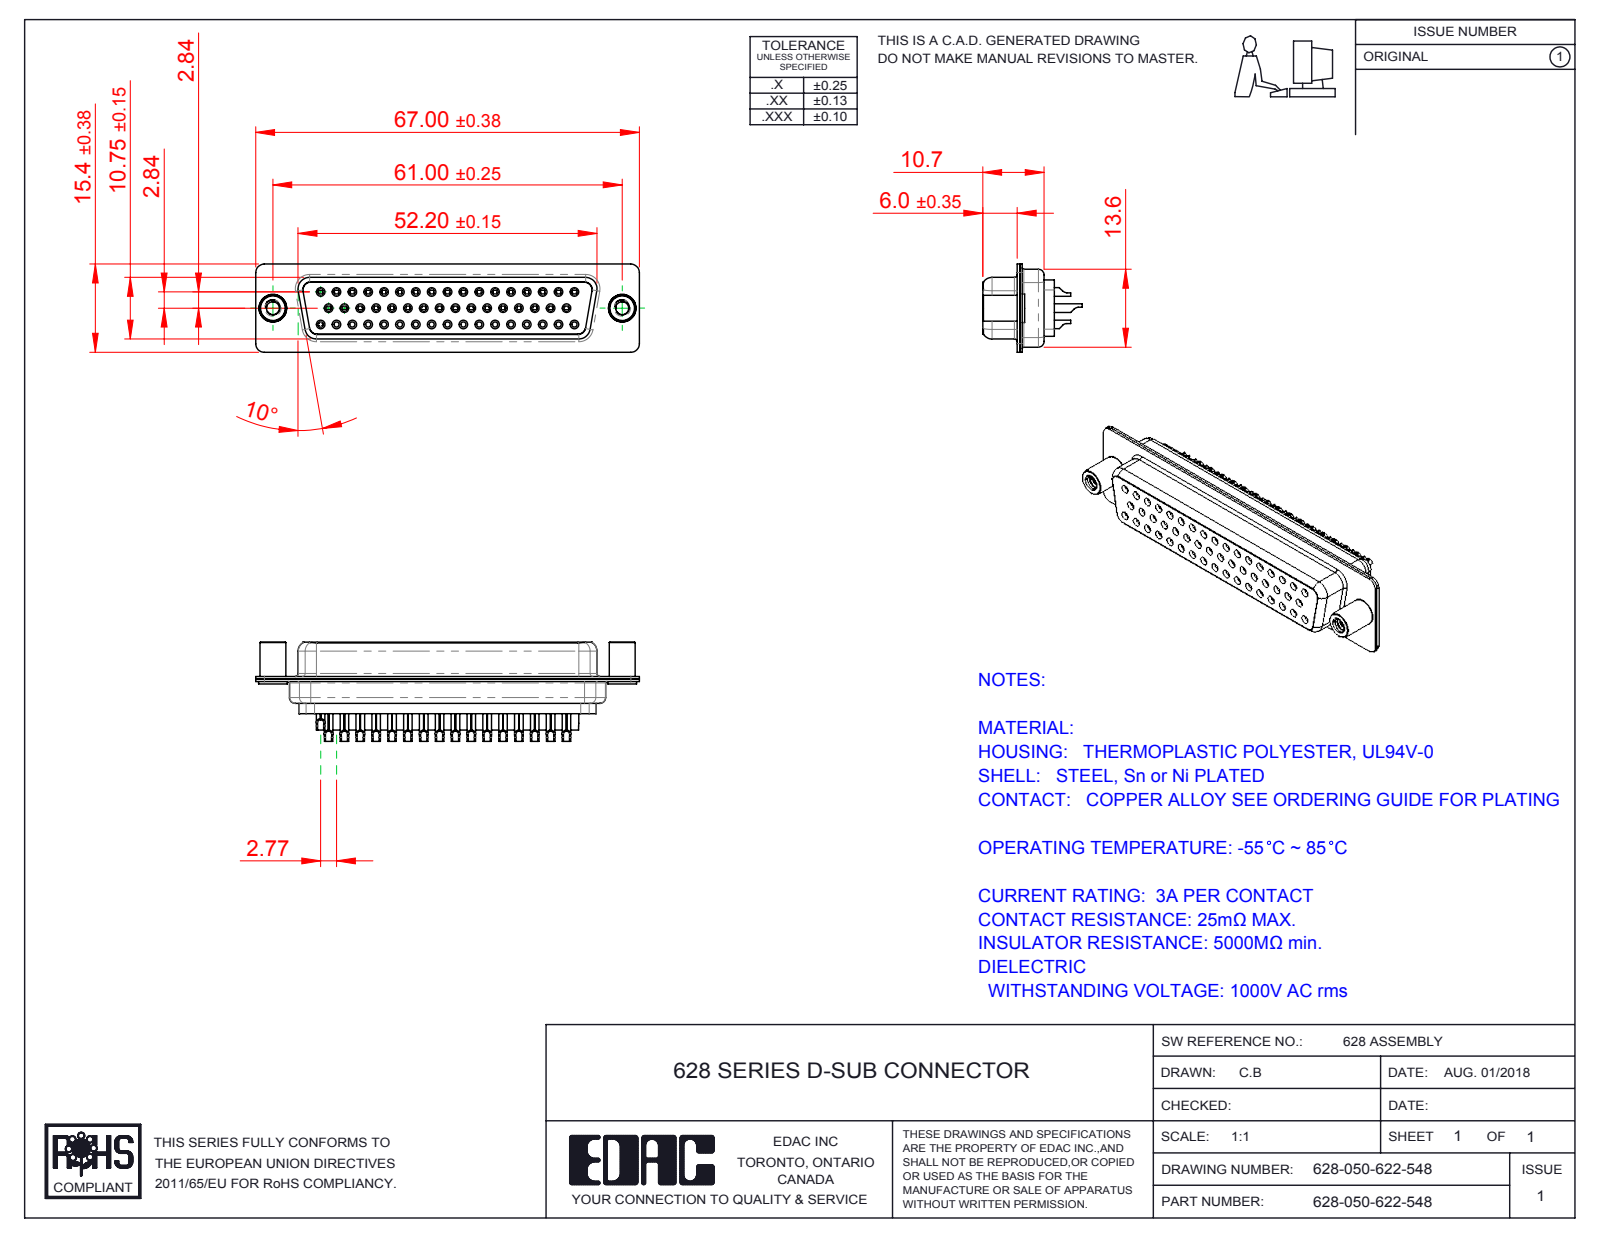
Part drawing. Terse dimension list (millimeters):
name: 628 Contact Row 3_22L; 628 Contact Row 2_22M; 628 Contact Row 1_22L; 628 Shell Rear_50 Contacts (+4 more)
written by: SolidWorks 2016 (CONFIG_CONTROL_DESIGN)
unit: mm
bodies: 39 solids, 3547 faces (831 planar, 1143 cylindrical, 1573 other)
size: 67 × 17.35 × 15.4
volume: 6 698 mm³; area: 14 325 mm²
holes: 50× ⌀0.9, 50× ⌀1.6, 34× ⌀0.8, 34× ⌀1.1, 17× ⌀1.7, 16× ⌀1.5, 16× ⌀2, 2× ⌀2.26, 2× ⌀4, 2× ⌀4.8
bosses: 34× ⌀2, 34× ⌀1.5, 34× ⌀1.2, 2× ⌀5, 2× ⌀4.9, 2× ⌀4.5
rounds: 33× R0.28, 16× R1.5, 12× R2, 8× R1.35, 7× R1, 4× R0.25, 4× R0.5, 4× R0.6
face distances: 0.45, 0.4, 0.9, 10.3, 6.05, 6.5, 12.5, 6.45, 6, 11.33
hole spacings: 3.16, 2.77, 5.54, 8.31, 11.08, 13.85, 16.62, 19.39
